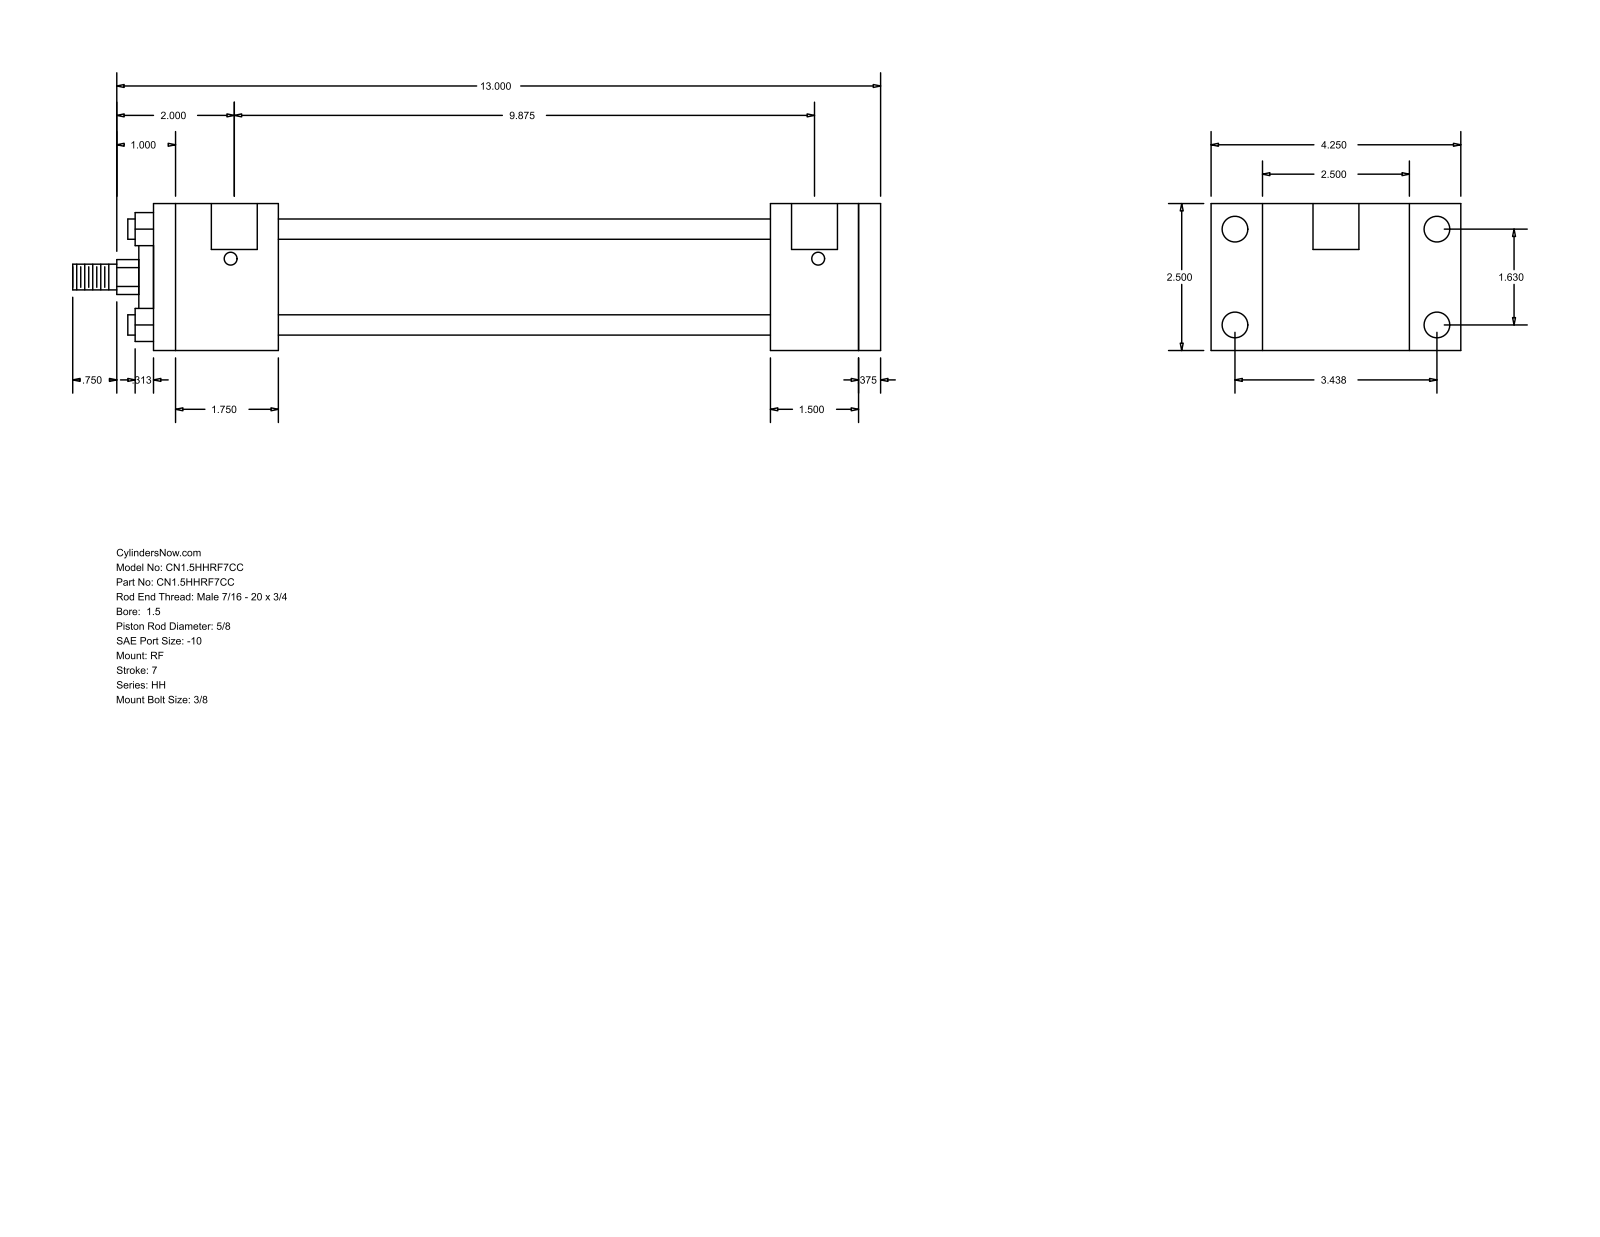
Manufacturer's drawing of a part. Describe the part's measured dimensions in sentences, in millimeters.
The part is named "HH_RF__0150_0.625". Its 3-D file was written by "GSSL Pune (CONFIG_CONTROL_DESIGN)". It is 0 solids with 92 faces: 64 planar, 28 cylindrical and 0 other. Overall it measures 349.25 by 107.95 by 63.5 millimeters. Round holes: 4 of diameter 5.56, 4 of diameter 11.13, 2 of diameter 19.84. Round bosses or shafts: 4 of diameter 8.76, 1 of diameter 44.45, 1 of diameter 28.57, 1 of diameter 15.88, 1 of diameter 11.11. Partial cylindrical surfaces (rounded edges, fillets, slot ends): 1 of radius 7.54. The main face-to-face distances are 63.5, 314.32, 304.8, 9.52, 47.63, 53.97, 266.69, 212.72, 250.83, 260.35. The hole center spacings are 1.59, 41.4, 87.32, 96.64, 252.41, 254, 250.82.
